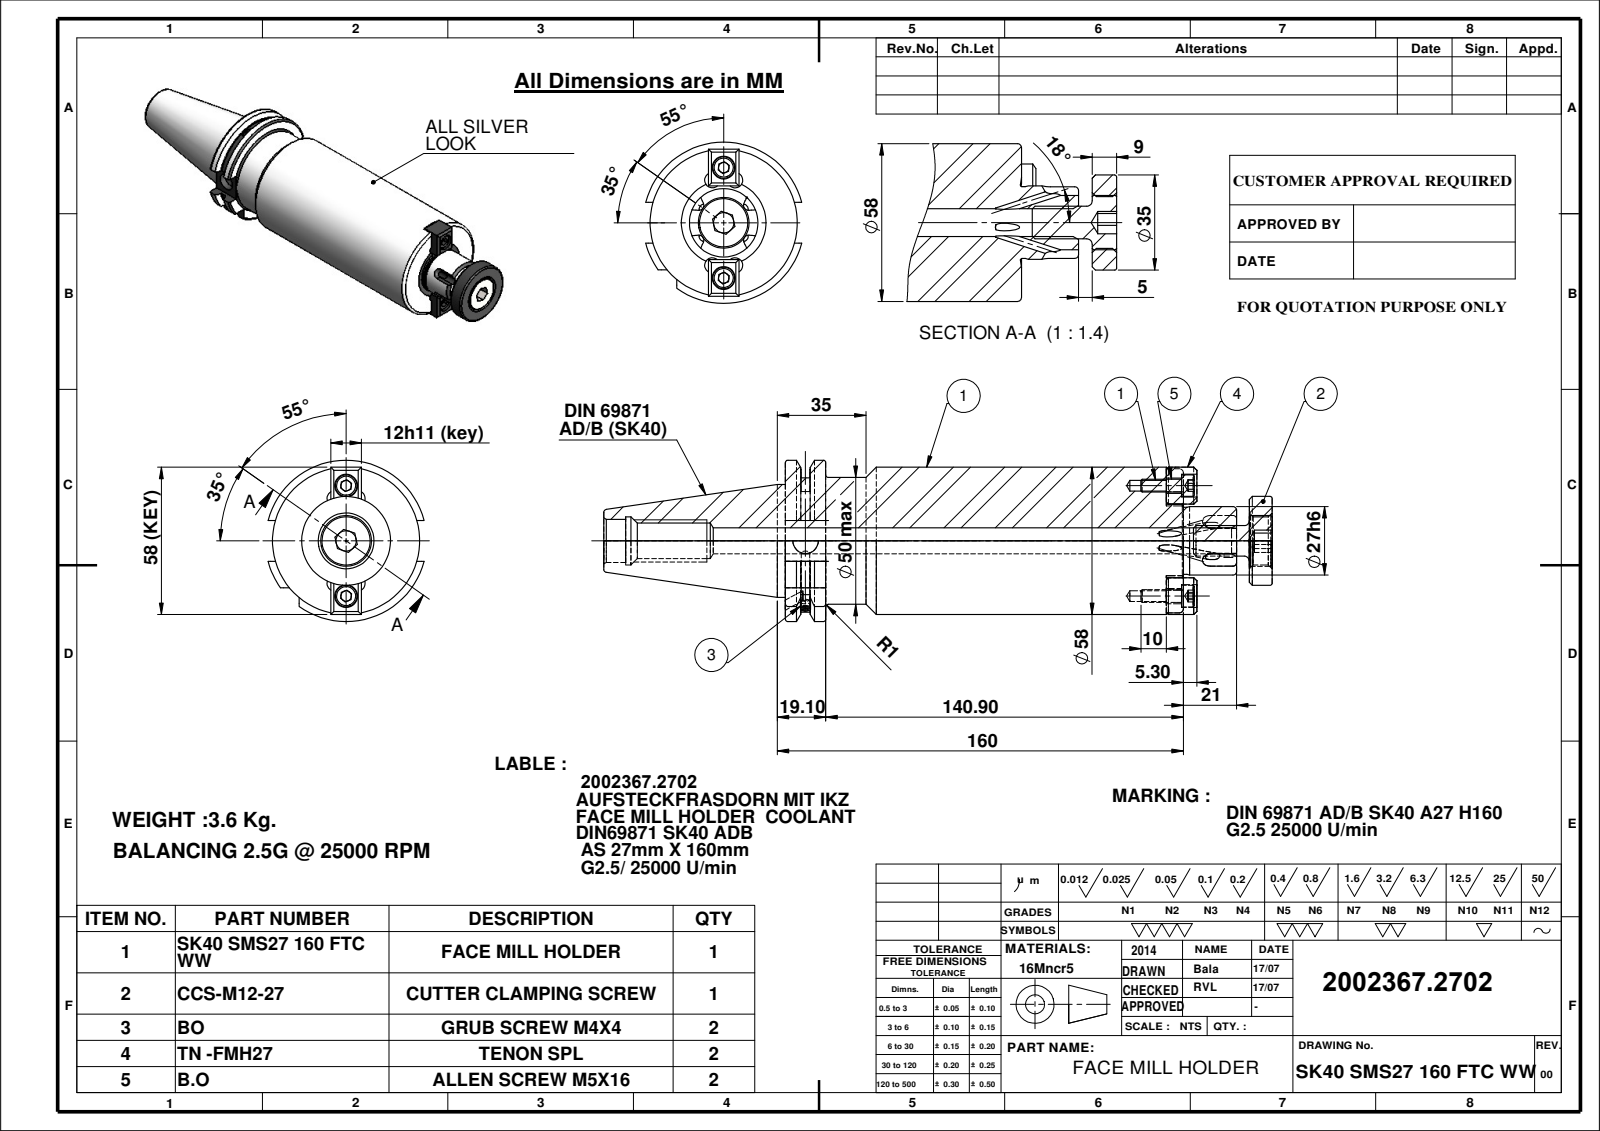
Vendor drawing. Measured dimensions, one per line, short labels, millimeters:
name: AS-M5X16_AS-M5X12; TN -FMH27; SK40 SMS27 160 FTC WW; CCS-M12-27-1 (+3 more)
written by: SolidWorks 2009 (CONFIG_CONTROL_DESIGN)
unit: mm
bodies: 9 solids, 349 faces (141 planar, 86 cylindrical, 122 other)
size: 263.4 × 63.55 × 61.48
volume: 470 828 mm³; area: 63 575 mm²
holes: 4× ⌀3, 2× ⌀4.2, 2× ⌀6, 2× ⌀9, 1× ⌀3.3, 1× ⌀10, 1× ⌀10.2, 1× ⌀14, 1× ⌀17, 1× ⌀19
bosses: 2× ⌀8.5, 2× ⌀5, 2× ⌀4, 1× ⌀58, 1× ⌀50, 1× ⌀44.45, 1× ⌀35, 1× ⌀27
rounds: 4× R2, 4× R3, 1× R28.12, 1× R31.77
face distances: 156.8, 191.8, 35, 15.9, 140.9, 175.9, 150.1, 134.2, 6.7, 41.7
hole spacings: 21.75, 43.5
